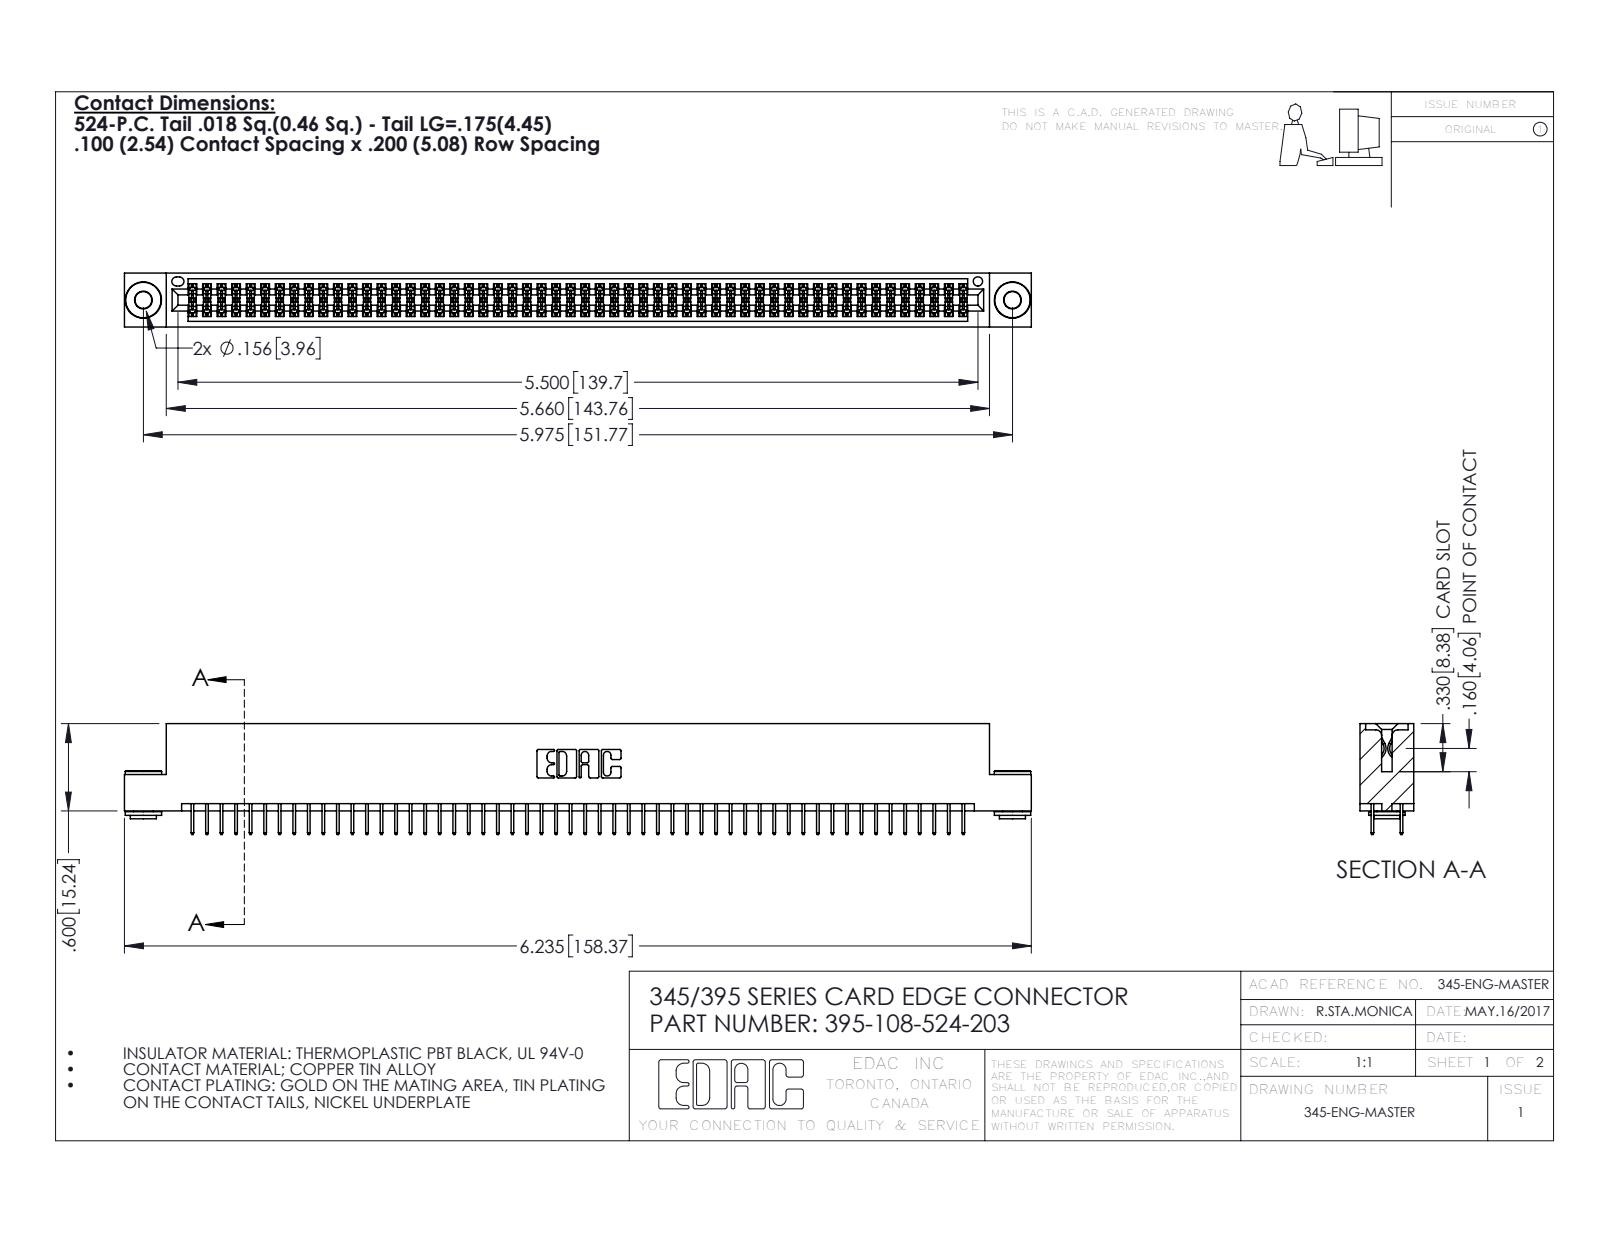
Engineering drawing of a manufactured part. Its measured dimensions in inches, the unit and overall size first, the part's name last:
Units: inches
Overall size (bounding box): 6.235 × 0.762 × 0.37
Round holes (diameter × count): ⌀0.116 ×2, ⌀0.156 ×2, ⌀0.064 ×1
Round bosses / shafts (diameter × count): ⌀0.25 ×2, ⌀0.18 ×2, ⌀0.136 ×2
Partial cylindrical surfaces — rounded edges, fillets, slot ends (radius × count): R0.006 ×162, R0.01 ×22, R0.007 ×6, R0.031 ×6, R0.026 ×3, R0.014 ×2, R0.019 ×2, R0.022 ×2
Main face-to-face distances: 0.072, 0.298, 0.2, 0.37, 0.025, 0.098, 0.272, 0.225, 0.072, 0.175
Hole centre spacings: 0.27, 5.739, 5.975
Volume: 0.937 in³ · Surface area: 35.18 in²
Bodies: 111 solids, 5996 faces (4302 planar, 1686 cylindrical, 8 other)
Part name (STEP PRODUCT): 345 Part_Flush Mounting Lugs - 0.156 Dia-TH; 345-250-002_345-250-002-102; 345-292-001_345-293-124; 395-108-524-203
STEP written by: SolidWorks 2016 (CONFIG_CONTROL_DESIGN)
